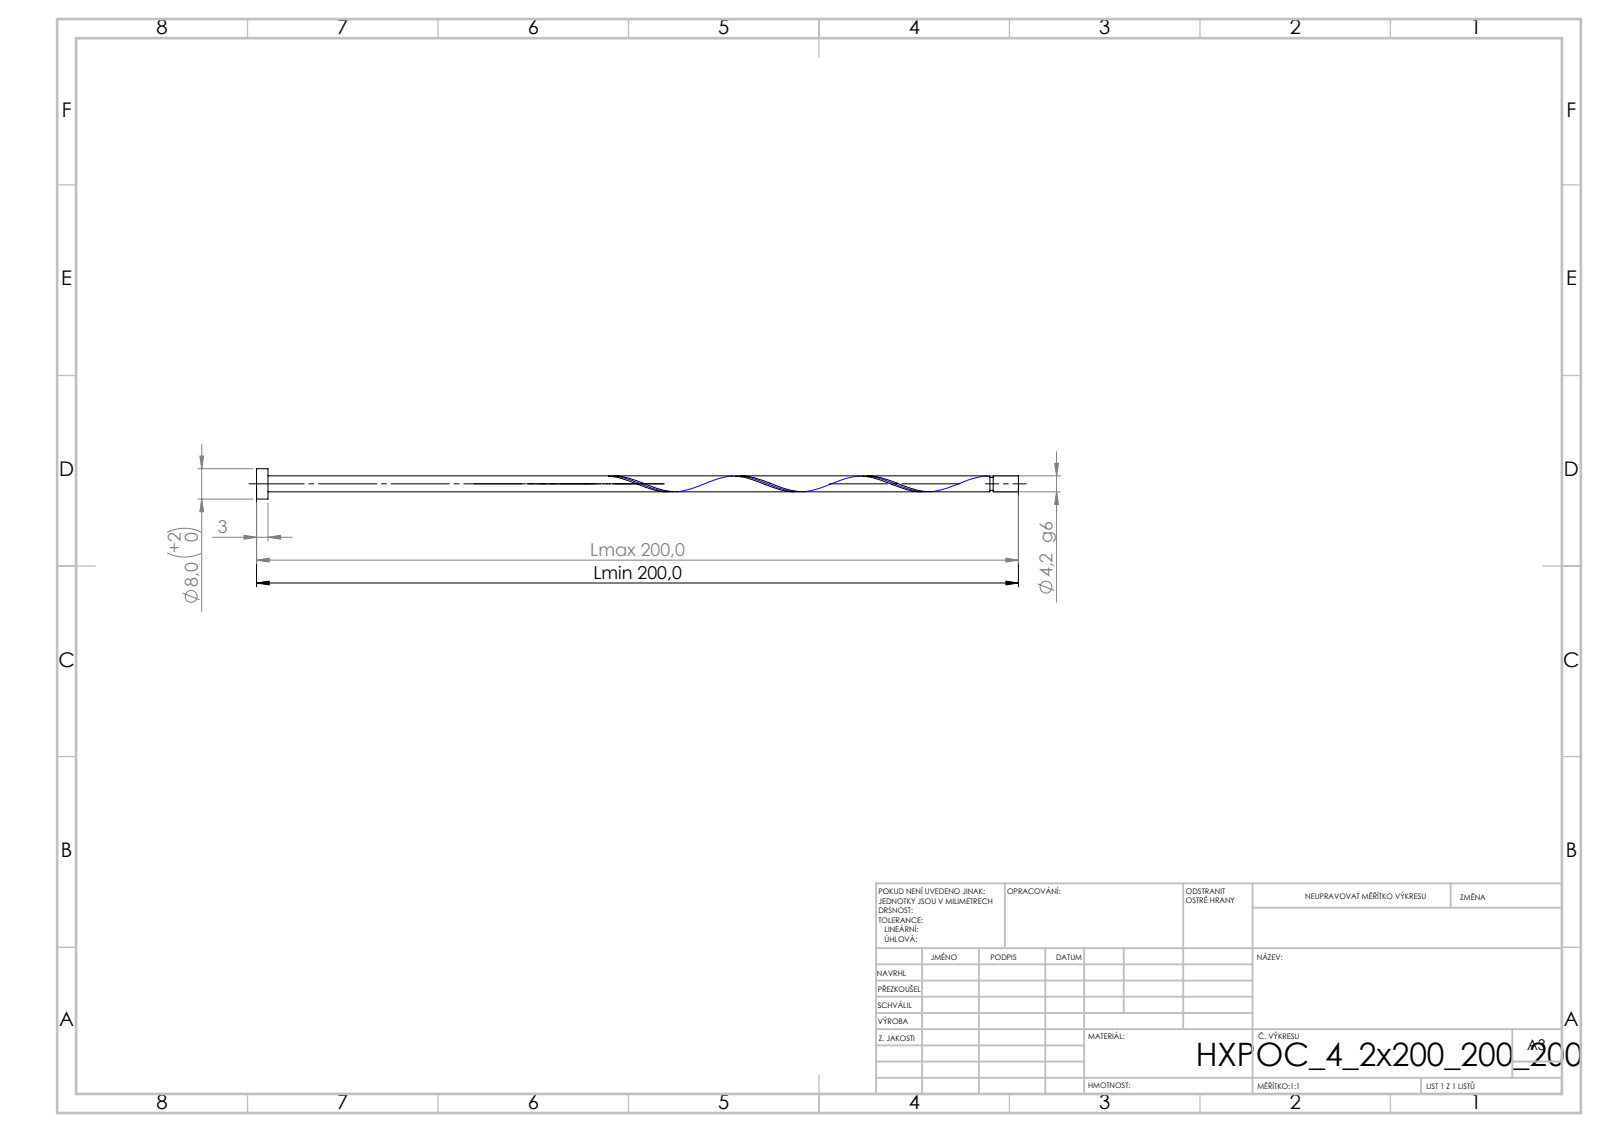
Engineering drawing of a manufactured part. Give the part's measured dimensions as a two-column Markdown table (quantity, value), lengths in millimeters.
| quantity | value |
| --- | --- |
| STEP written by | SolidWorks 2019 (CONFIG_CONTROL_DESIGN) |
| units | millimeters |
| bodies | 1 solid, 21 faces (6 planar, 14 cylindrical, 1 other) |
| overall size | 200 × 8 × 8 |
| volume | 2 849 mm³ |
| surface area | 2 827 mm² |
| round bosses / shafts (diameter × count) | 8 × 1, 4.2 × 1, 3.36 × 1 |
| main face-to-face distances | 3, 200, 197, 193.34, 190.34, 6.66, 192.5, 189.5, 0.84, 7.5 |
